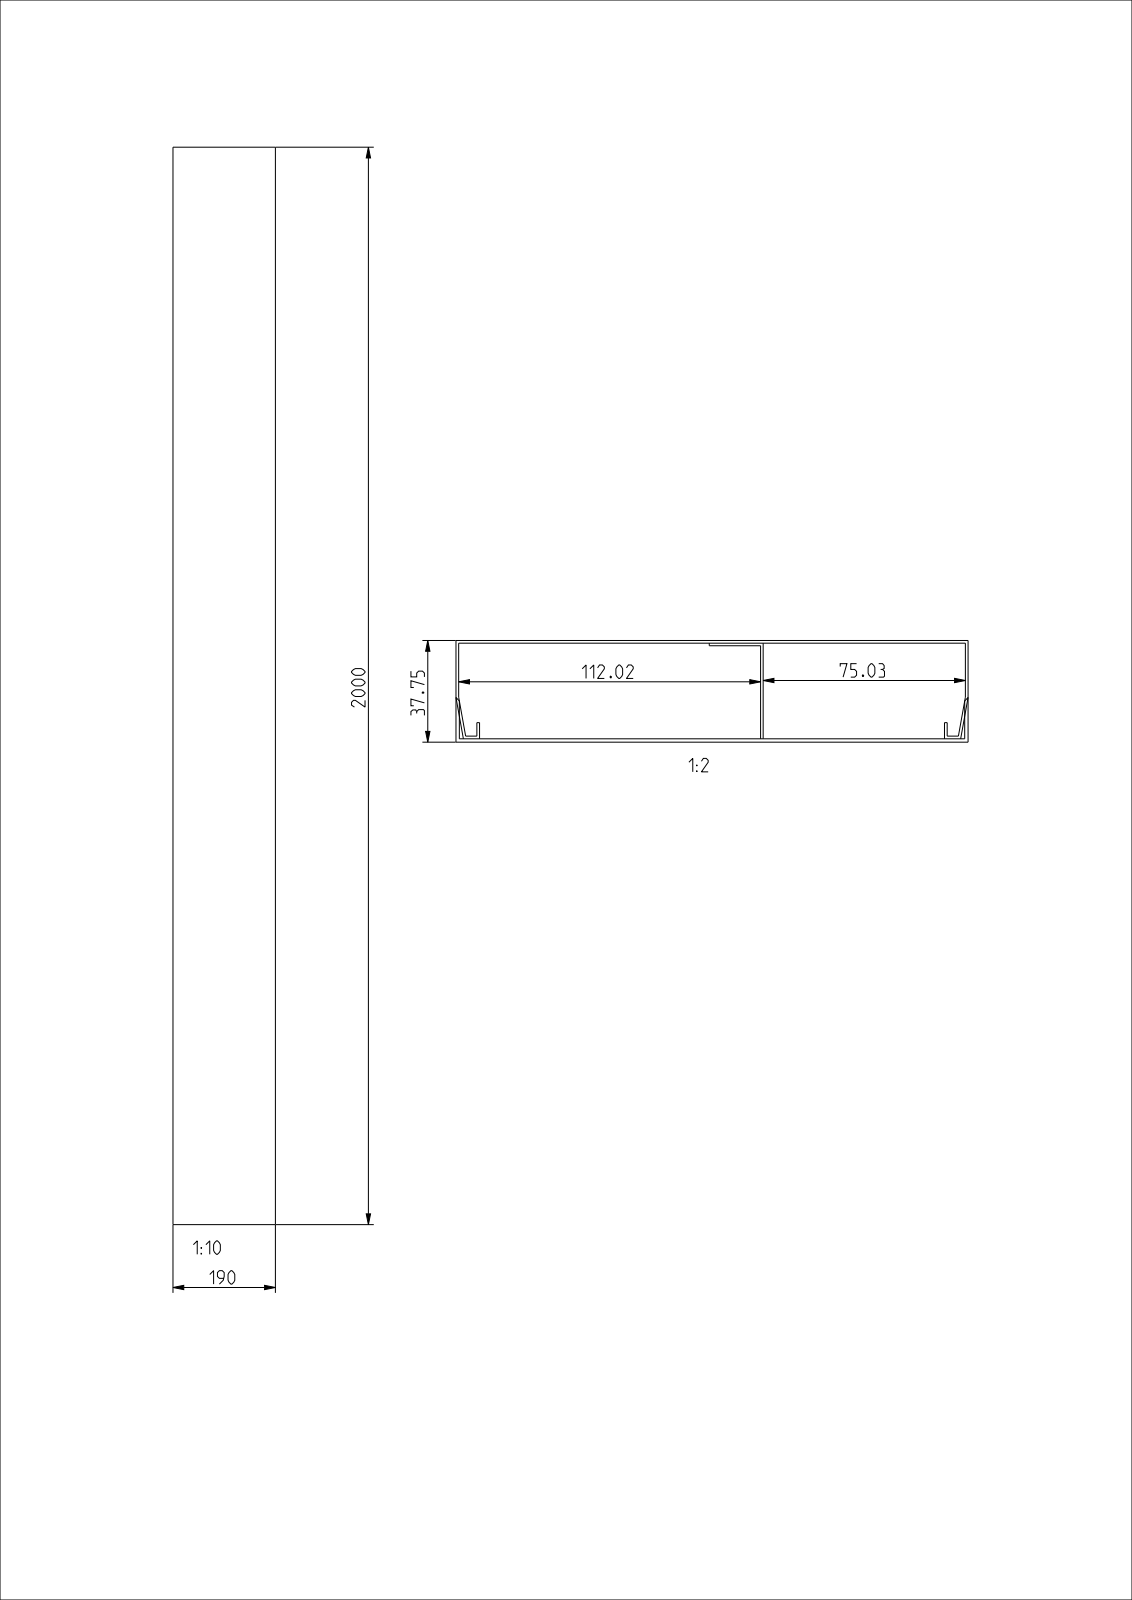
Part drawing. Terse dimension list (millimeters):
name: UK190382KUN_OBERTEIL; UK190382KUN_UNTERTEIL; UK190382KUN_ASM
written by: CREO PARAMETRIC BY PTC INC, 2022024 (AUTOMOTIVE_DESIGN)
unit: mm
bodies: 2 solids, 39 faces (39 planar, 0 cylindrical, 0 other)
size: 2000 × 190 × 37.75
volume: 1 216 000 mm³; area: 2 158 000 mm²
face distances: 1, 1.25, 36.5, 37.75, 35.5, 36.75, 189, 190, 113.97, 76.03
